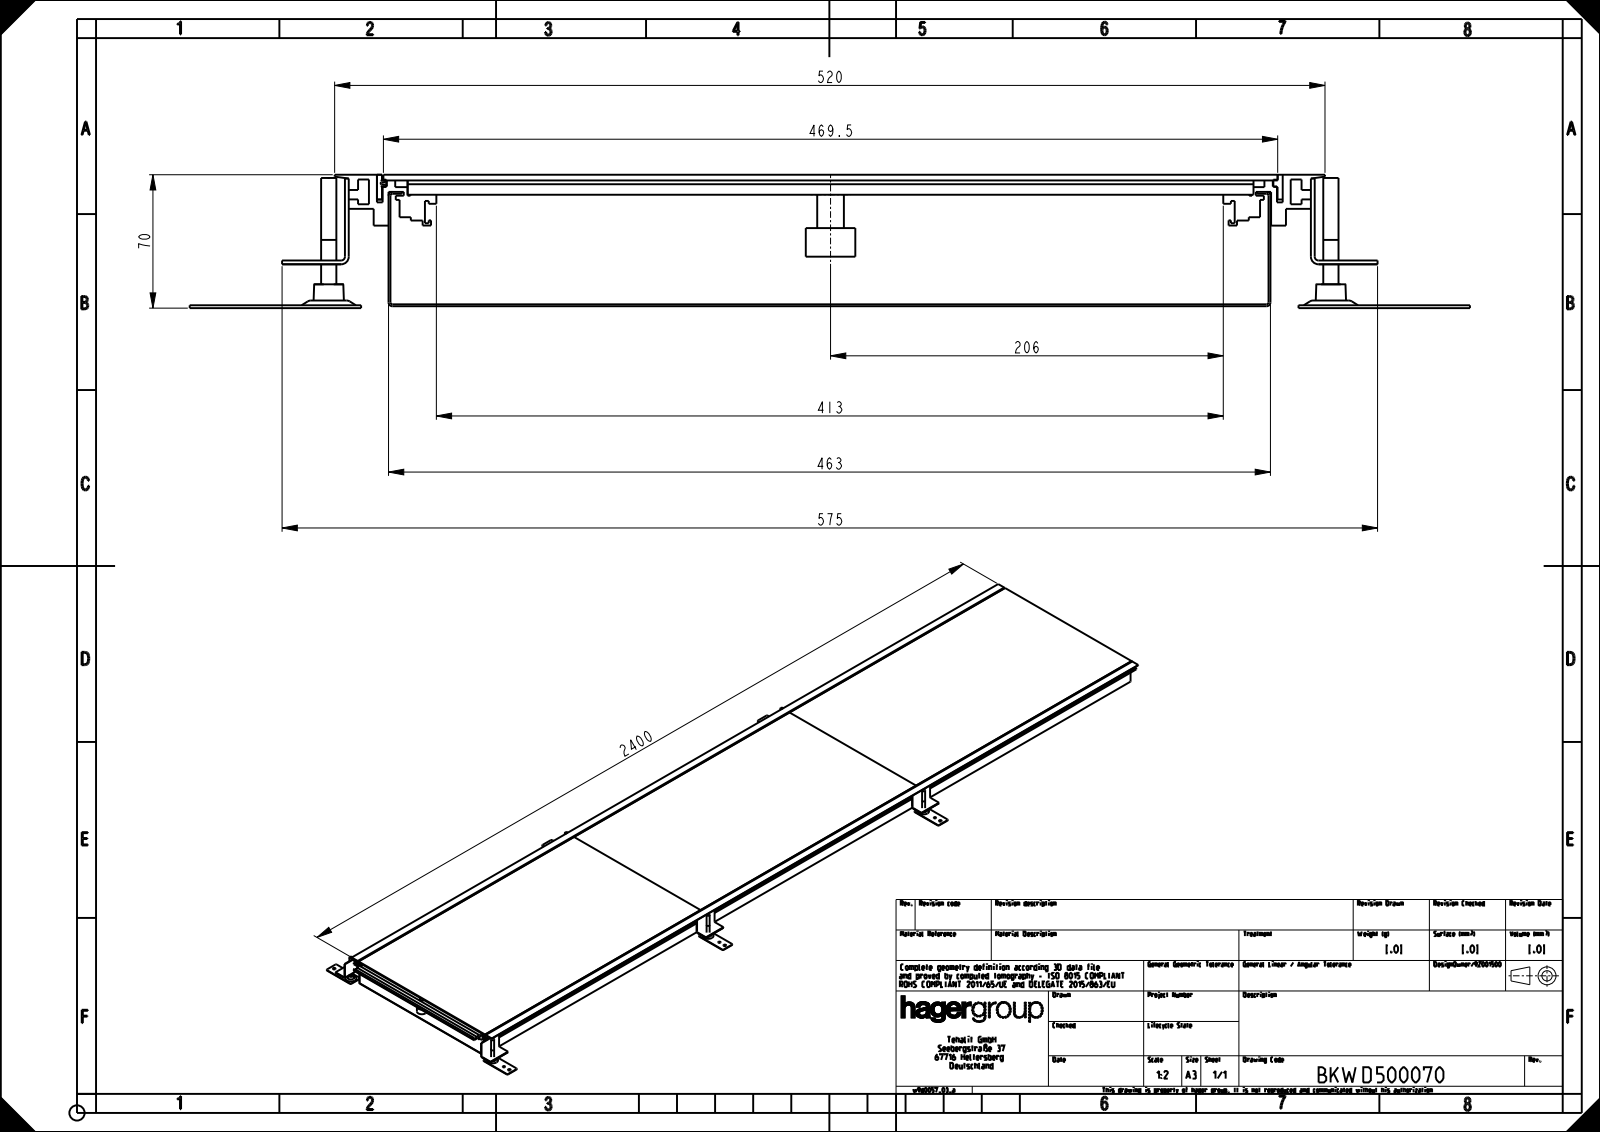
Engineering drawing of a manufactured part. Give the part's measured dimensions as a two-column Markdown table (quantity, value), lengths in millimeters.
| quantity | value |
| --- | --- |
| part name | U05644KUN; U05650KUN; U05647KUN; U05826KUN (+8 more) |
| STEP written by | CREO PARAMETRIC BY PTC INC, 2020281 (AUTOMOTIVE_DESIGN) |
| units | millimeters |
| bodies | 61 solids, 1036 faces (606 planar, 358 cylindrical, 72 other) |
| overall size | 2432.5 × 672.13 × 70 |
| volume | 9 085 000 mm³ |
| surface area | 7 489 000 mm² |
| round holes (diameter × count) | 7 × 15, 8 × 9, 10 × 9, 6 × 6, 8.5 × 6, 11.5 × 6, 17.5 × 6, 23 × 6 |
| round bosses / shafts (diameter × count) | 26 × 9, 14 × 9, 11.9 × 9, 20 × 6, 8 × 6 |
| partial cylindrical surfaces (radius × count) | 2 × 96, 3 × 24, 0.5 × 20, 1 × 4, 4 × 2 |
| main face-to-face distances | 1, 3, 65, 66, 69, 68, 7.5, 462, 6.5, 58.5 |
| hole center spacings | 800, 1600, 800.25, 801.1, 802.4, 981.21, 992.92, 1018.36 |
